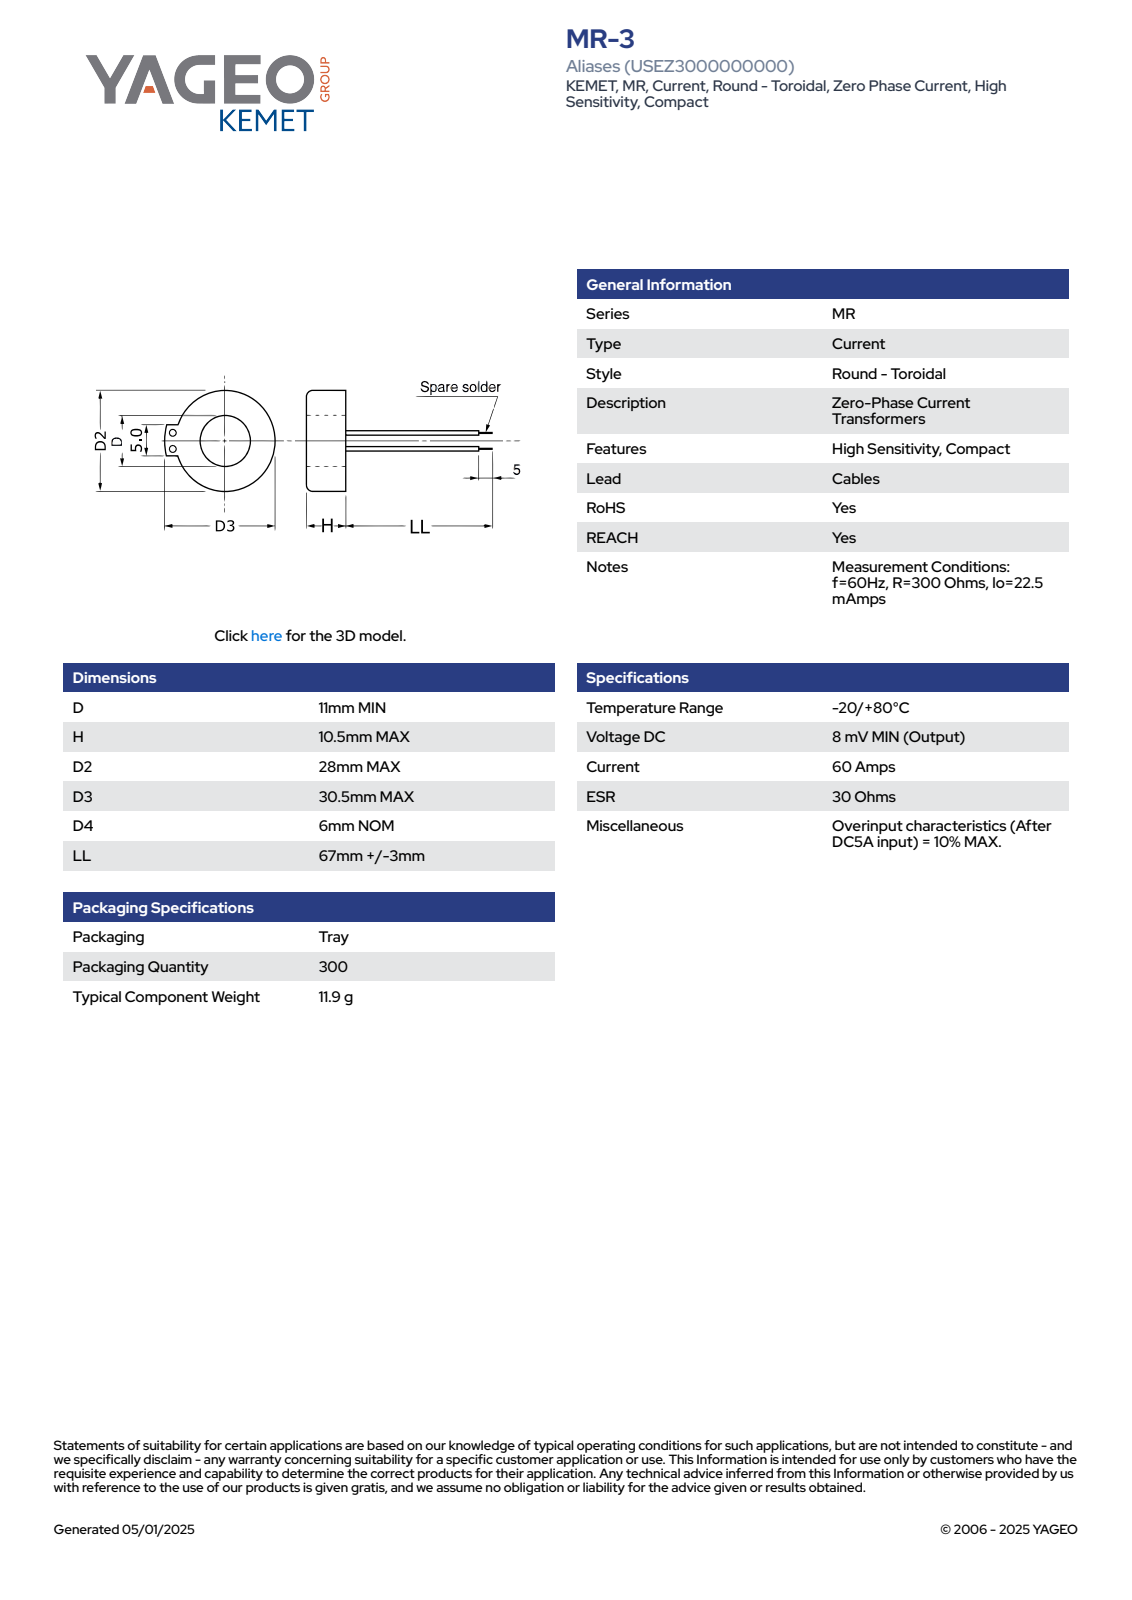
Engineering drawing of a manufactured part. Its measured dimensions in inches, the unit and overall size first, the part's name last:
Units: inches
Overall size (bounding box): 3.169 × 1.201 × 1.102
Round holes (diameter × count): ⌀0.433 ×1
Round bosses / shafts (diameter × count): ⌀0.039 ×2, ⌀0.026 ×2, ⌀1.102 ×1
Partial cylindrical surfaces — rounded edges, fillets, slot ends (radius × count): R0.039 ×2, R0.551 ×1
Main face-to-face distances: 0.413, 0.236, 2.972, 2.559, 0.197, 2.756, 3.169, 0.167, 0.246, 3.002
Volume: 0.349 in³ · Surface area: 4.342 in²
Bodies: 1 solid, 84 faces (30 planar, 18 cylindrical, 36 other)
Part name (STEP PRODUCT): SC_MR1_D11H10.5D228D330.5D46LL70
STEP written by: SolidWorks 2014 (AUTOMOTIVE_DESIGN)
